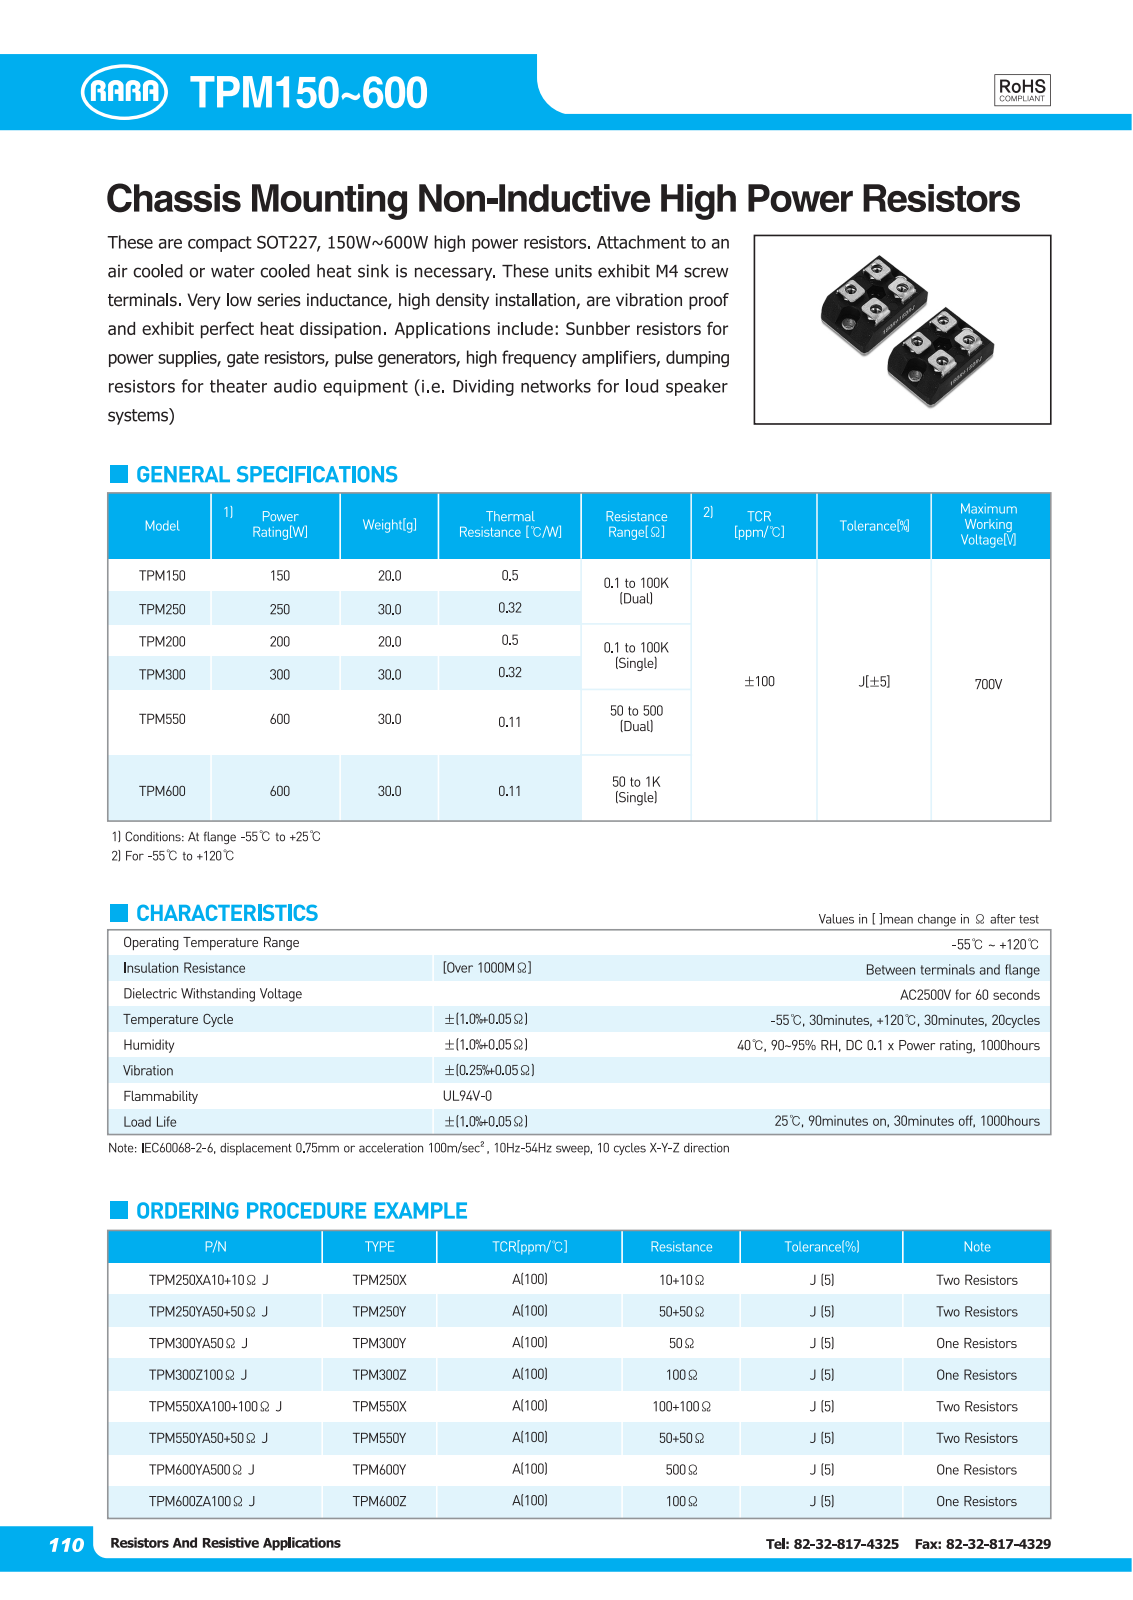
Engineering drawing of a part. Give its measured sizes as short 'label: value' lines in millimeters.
written by: Unknown (CONFIG_CONTROL_DESIGN)
unit: mm
bodies: 12 solids, 358 faces (300 planar, 28 cylindrical, 30 other)
size: 38 × 25 × 12.3
volume: 12 864 mm³; area: 11 769 mm²
holes: 4× ⌀4.2, 2× ⌀2, 2× ⌀3.2, 2× ⌀3.24
rounds: 3× R0.2, 3× R0.8, 1× R2.1
face distances: 2, 5.9, 8, 3.9, 2.1, 1, 7.9, 6, 4, 23
hole spacings: 7.62, 15, 19.53, 9.76, 12.5, 15.75, 22.54, 23.35
